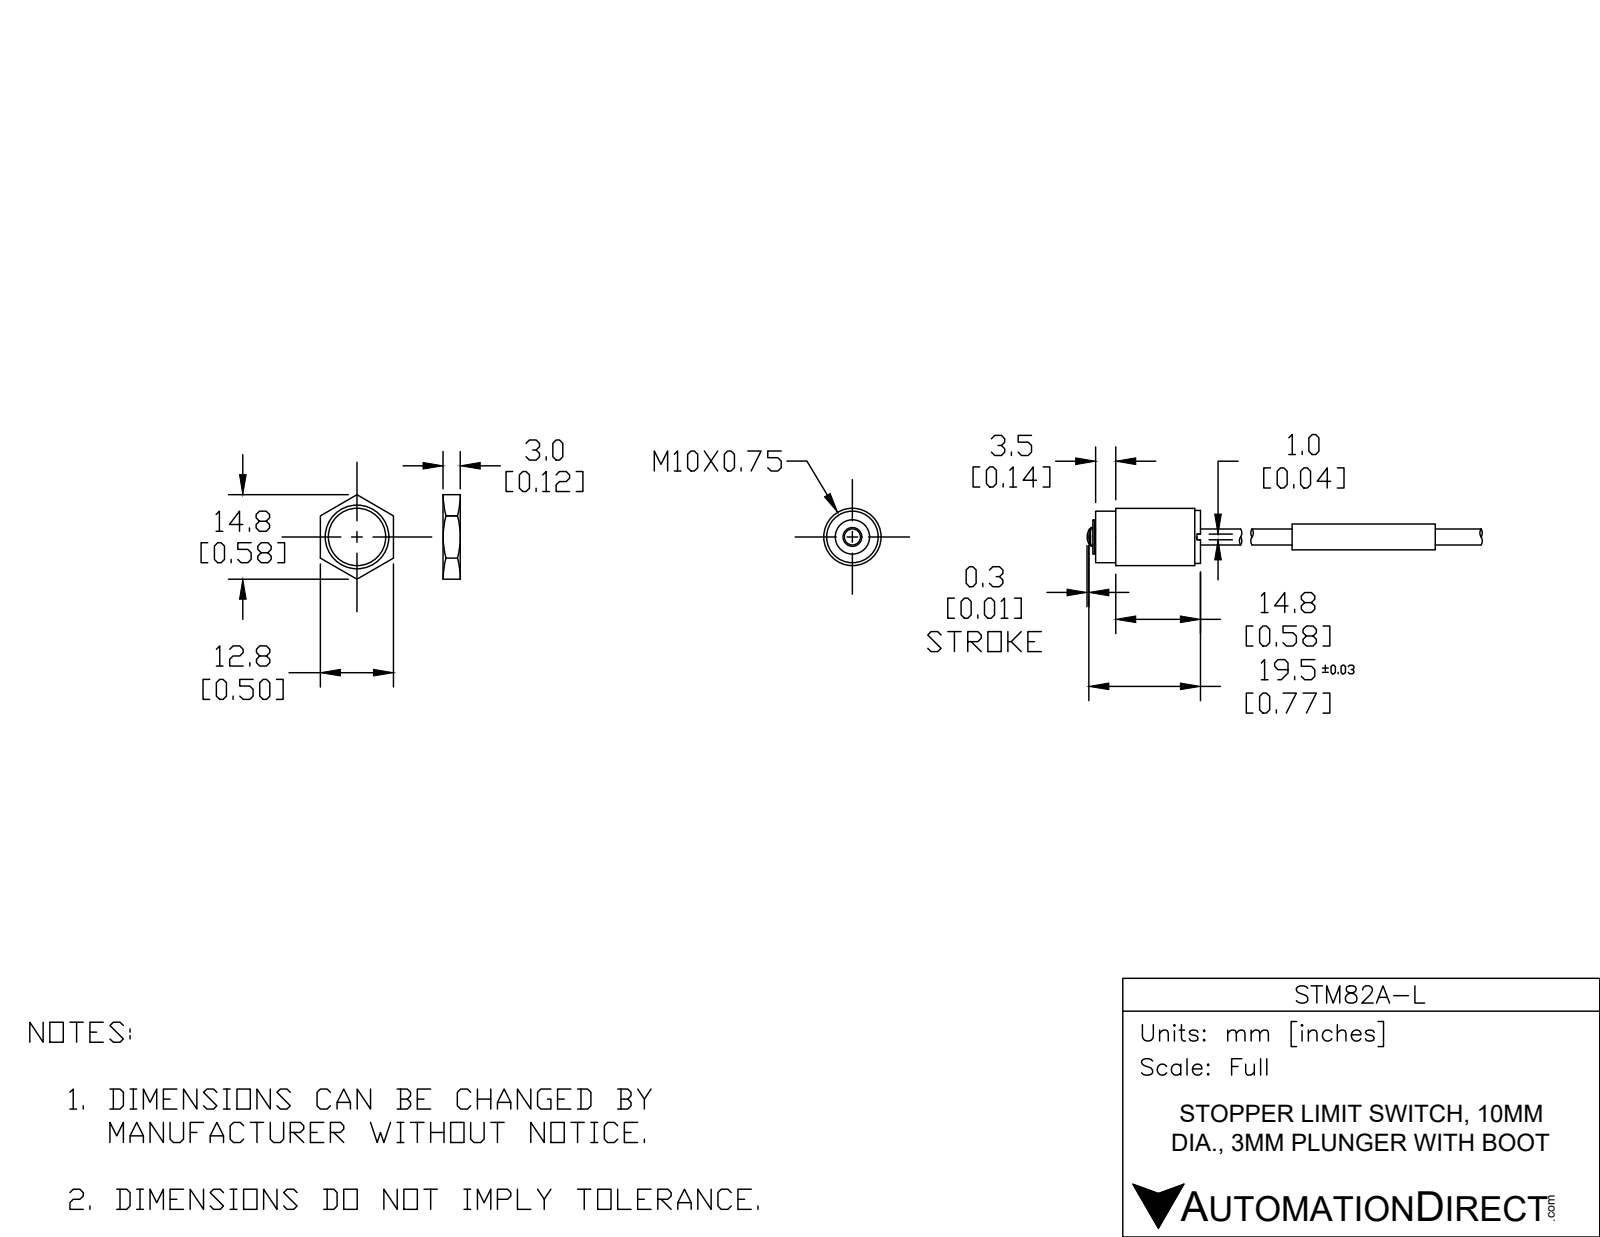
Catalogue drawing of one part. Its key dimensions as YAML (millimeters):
part_name: "STM82A-L"
step_written_by: "SolidWorks 2017 (CONFIG_CONTROL_DESIGN)"
units: millimeters
bodies: {solids: 2, faces: 83, planar: 20, cylindrical: 56, other: 7}
overall_size: [70.8, 10, 10]
volume: 1809
surface_area: 1623
round_bosses_or_shafts:
  - {diameter: 10, count: 1}
  - {diameter: 9, count: 1}
  - {diameter: 8.5, count: 1}
  - {diameter: 6, count: 1}
  - {diameter: 4.5, count: 1}
  - {diameter: 2.8, count: 1}
face_to_face_distances: [18.3, 18.5, 0.5, 18.8, 1, 4.4, 4.7, 4.2, 14.1, 17.8]
